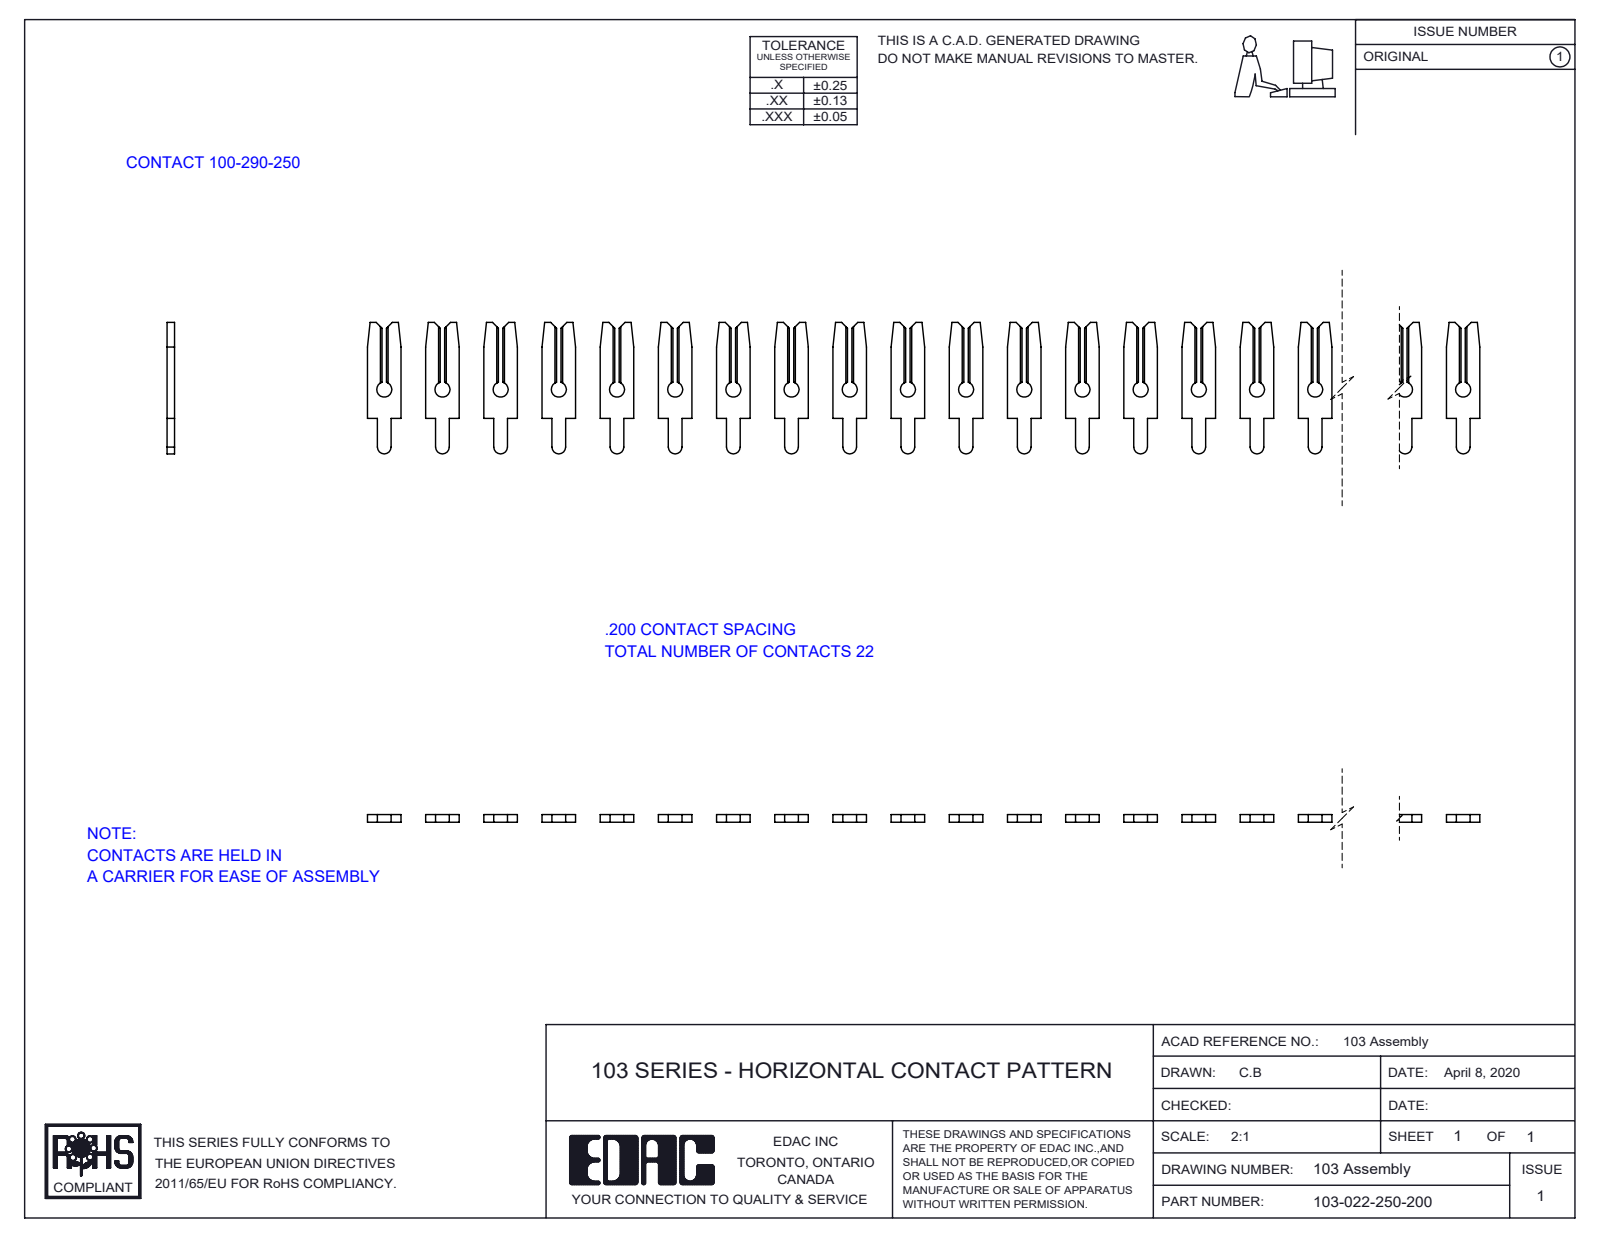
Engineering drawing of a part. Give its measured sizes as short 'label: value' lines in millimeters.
name: 103-022-250-200; 100-290-001_100-290-250
written by: SolidWorks 2016 (CONFIG_CONTROL_DESIGN)
unit: mm
bodies: 22 solids, 528 faces (440 planar, 88 cylindrical, 0 other)
size: 109.6 × 11.5 × 0.7
volume: 340 mm³; area: 1 614 mm²
holes: 22× ⌀1.3
rounds: 22× R0.6
face distances: 0.7, 3.6, 5.1, 10.2, 7.2, 21.5, 15.2, 25.1, 18, 20.3
hole spacings: 5.1, 10.2, 15.2, 20.3, 25.4, 30.5, 35.6, 40.6
